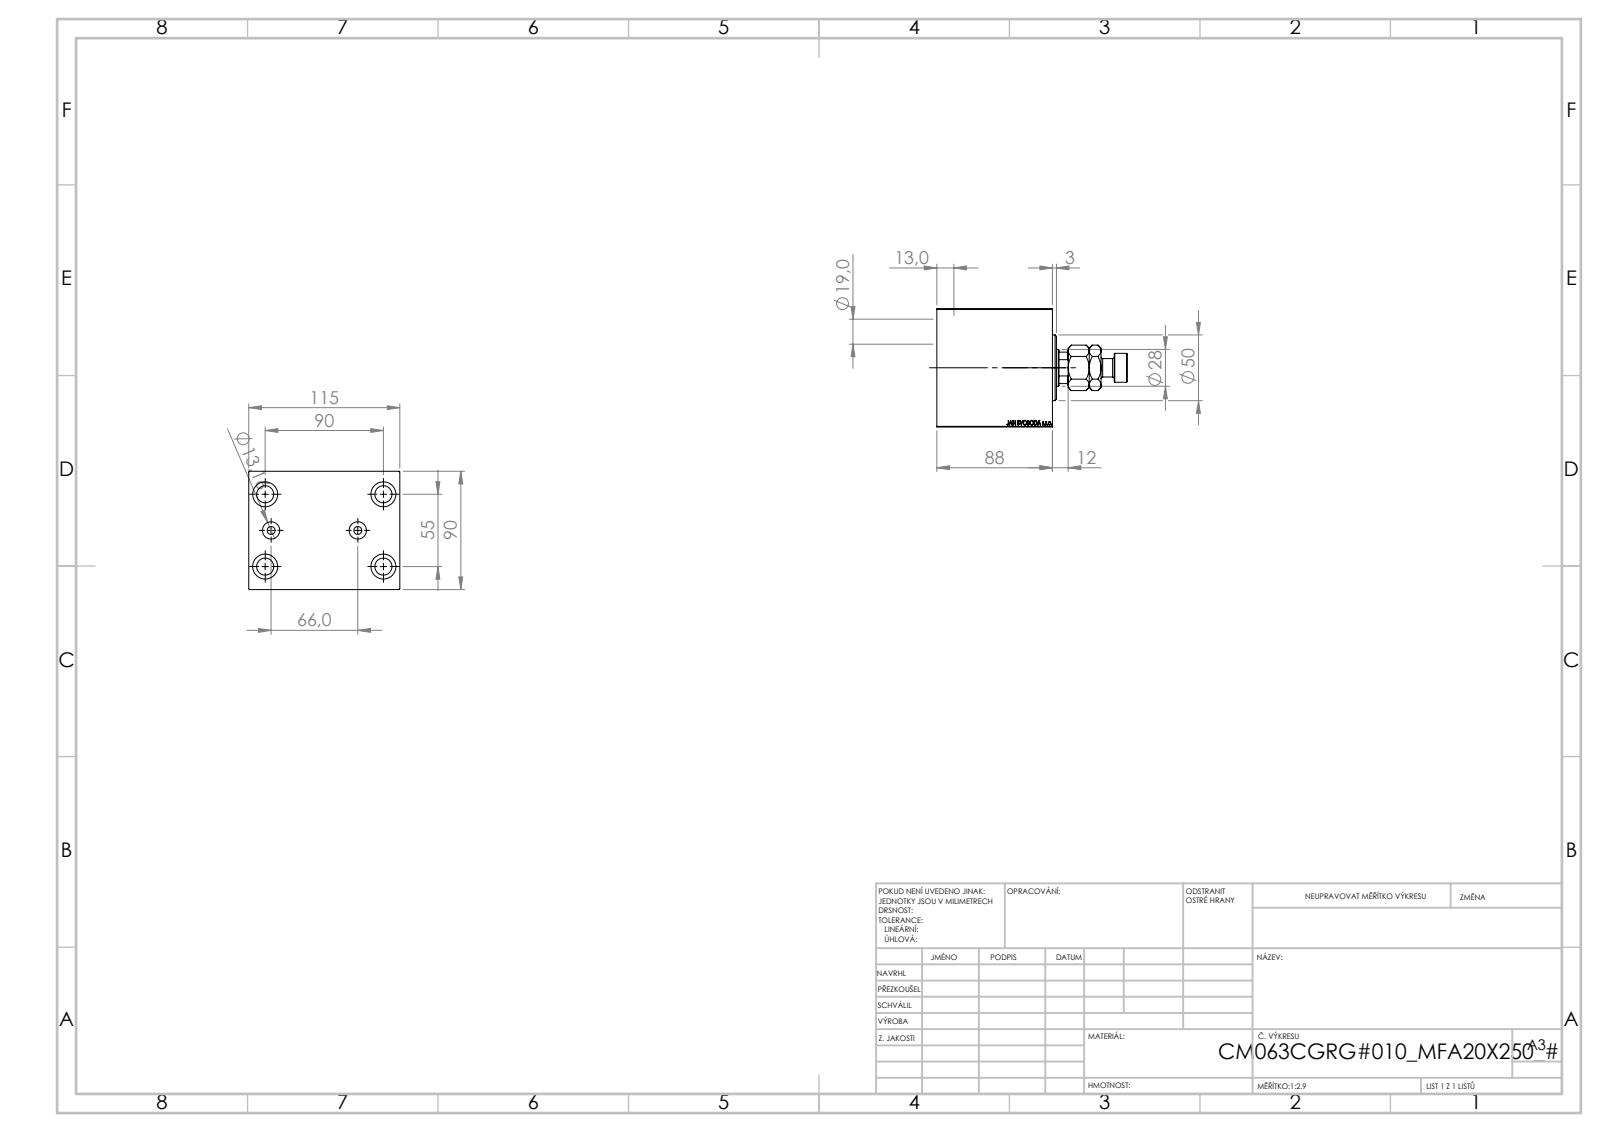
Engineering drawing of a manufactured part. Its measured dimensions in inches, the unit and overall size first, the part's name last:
Units: inches
Overall size (bounding box): 5.768 × 4.528 × 3.543
Round holes (diameter × count): ⌀0.512 ×4, ⌀0.748 ×4, ⌀0.236 ×2, ⌀0.518 ×2, ⌀0.728 ×1, ⌀1.102 ×1, ⌀1.24 ×1, ⌀2.48 ×1, ⌀2.559 ×1, ⌀2.835 ×1
Round bosses / shafts (diameter × count): ⌀1.969 ×1, ⌀0.866 ×1, ⌀0.551 ×1
Partial cylindrical surfaces — rounded edges, fillets, slot ends (radius × count): R0.531 ×1
Main face-to-face distances: 3.543, 4.528, 3.465, 1.654, 1.811, 0.394, 3.071, 0.197, 1.26, 0.787
Hole centre spacings: 1.181, 2.076, 3.256, 1.299, 2.165, 3.543, 4.153, 2.598
Volume: 51.6 in³ · Surface area: 177 in²
Bodies: 4 solids, 913 faces (425 planar, 62 cylindrical, 426 other)
Part name (STEP PRODUCT): V450CM_C_VCP; V450CM_VC_B; V450CM_C_Body; MFA
STEP written by: SolidWorks 2019 (CONFIG_CONTROL_DESIGN)
